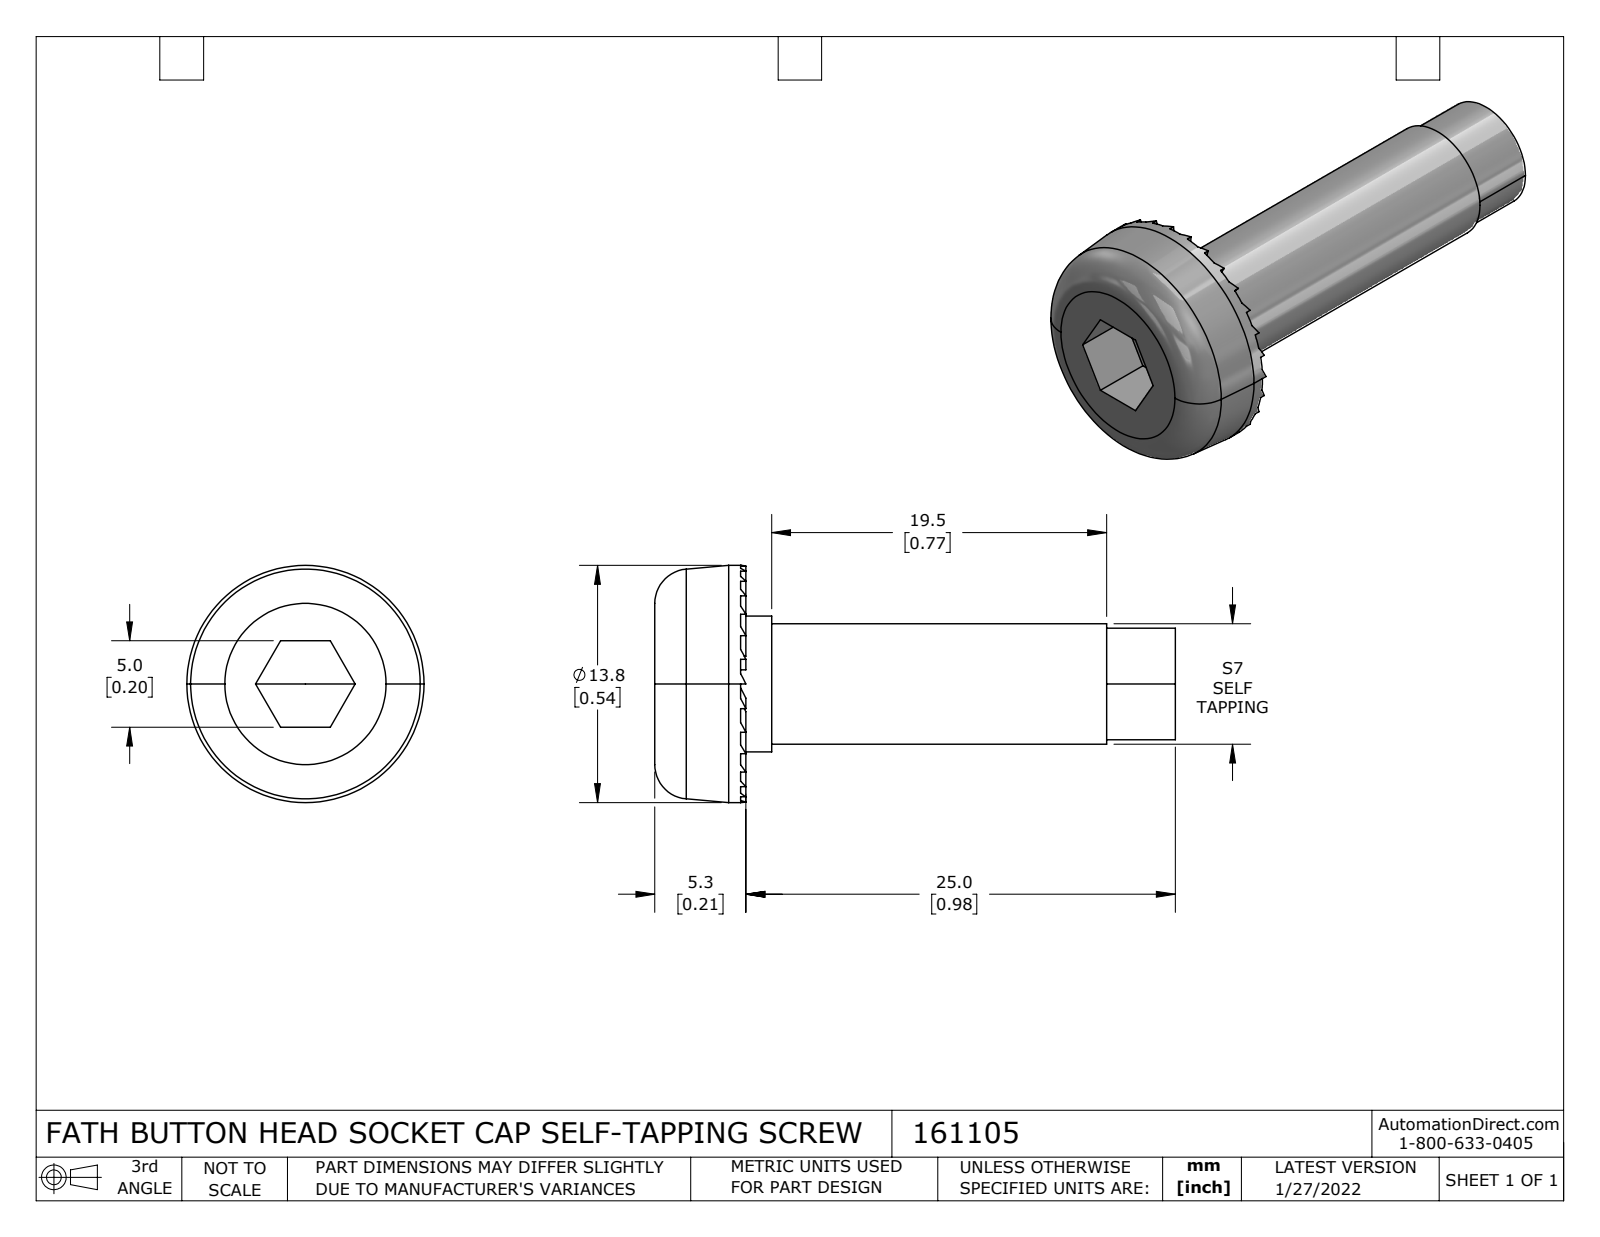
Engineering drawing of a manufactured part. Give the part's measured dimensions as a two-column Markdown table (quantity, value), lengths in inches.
| quantity | value |
| --- | --- |
| part name | 161105 |
| STEP written by | SolidWorks 2021 (CONFIG_CONTROL_DESIGN) |
| units | inches |
| bodies | 1 solid, 120 faces (106 planar, 8 cylindrical, 6 other) |
| overall size | 1.193 × 0.543 × 0.543 |
| volume | 0.096 in³ |
| surface area | 1.748 in² |
| round bosses / shafts (diameter × count) | 0.543 × 1, 0.311 × 1, 0.276 × 1, 0.256 × 1 |
| main face-to-face distances | 0.197, 0.996, 1.193, 0.198, 0.099, 0.925, 0.071, 0.268, 0.157, 0.768 |
